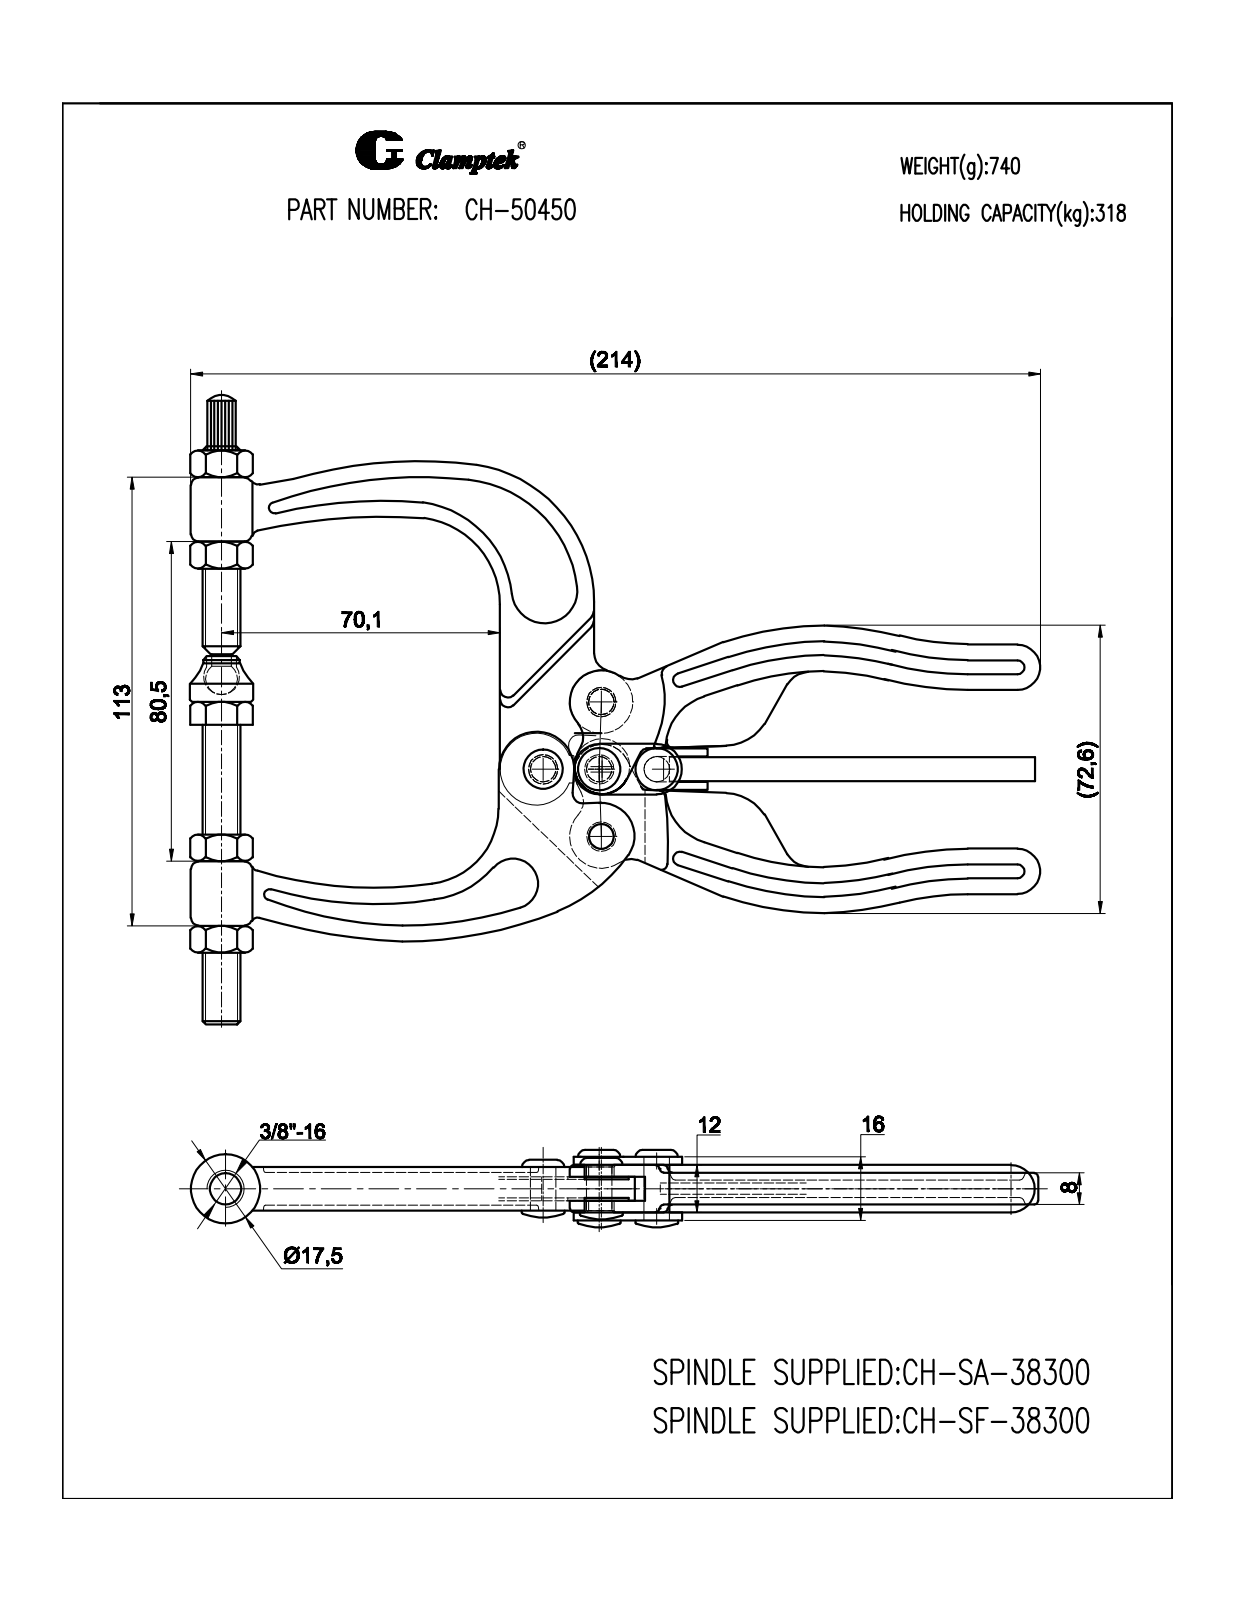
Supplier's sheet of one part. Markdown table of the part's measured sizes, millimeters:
| quantity | value |
| --- | --- |
| part name | CH-50450 |
| STEP written by | SolidWorks 2008 (CONFIG_CONTROL_DESIGN) |
| units | millimeters |
| bodies | 20 solids, 1562 faces (362 planar, 539 cylindrical, 661 other) |
| overall size | 214.55 × 159.13 × 20 |
| volume | 96 765 mm³ |
| surface area | 54 493 mm² |
| round holes (diameter × count) | 6.4 × 5, 8 × 2, 8.5 × 2, 7.8 × 1 |
| round bosses / shafts (diameter × count) | 9 × 5, 17.5 × 2, 9.5 × 2, 17.87 × 1, 16.8 × 1, 16 × 1 |
| partial cylindrical surfaces (radius × count) | 0.5 × 52, 1 × 29, 1.5 × 8, 0.2 × 5, 7 × 4, 12 × 4, 4.99 × 2, 5 × 2 |
| main face-to-face distances | 3, 9, 2.25, 12, 2, 11.75, 8.75, 3.3, 6, 7.15 |
| hole center spacings | 14.35, 14.5, 16.9, 16.91, 22.07, 22.08, 22.34, 22.4 |
